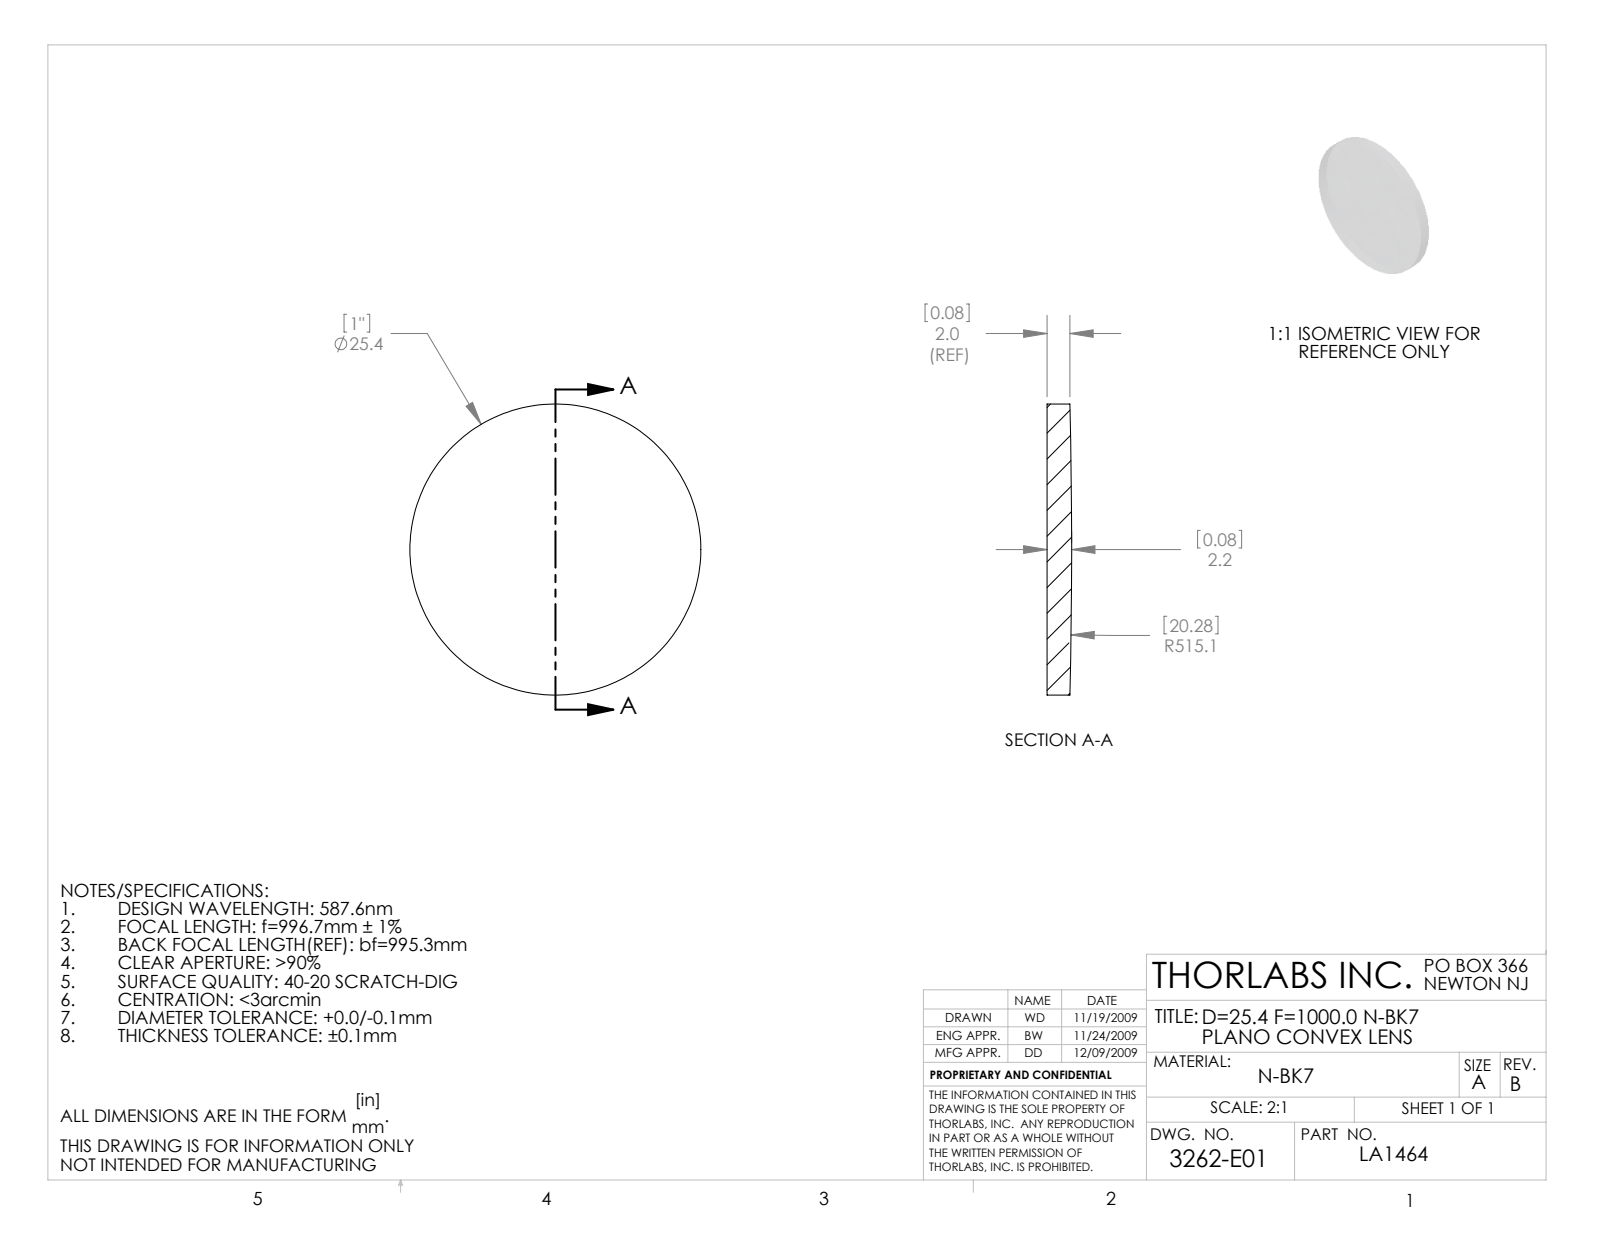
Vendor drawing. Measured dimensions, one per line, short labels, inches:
name: 3262-E0W
written by: SolidWorks 2009 (AUTOMOTIVE_DESIGN)
unit: in
bodies: 1 solid, 5 faces (1 planar, 2 cylindrical, 2 other)
size: 1 × 1 × 0.085
volume: 0.064 in³; area: 1.818 in²
bosses: 1× ⌀1
